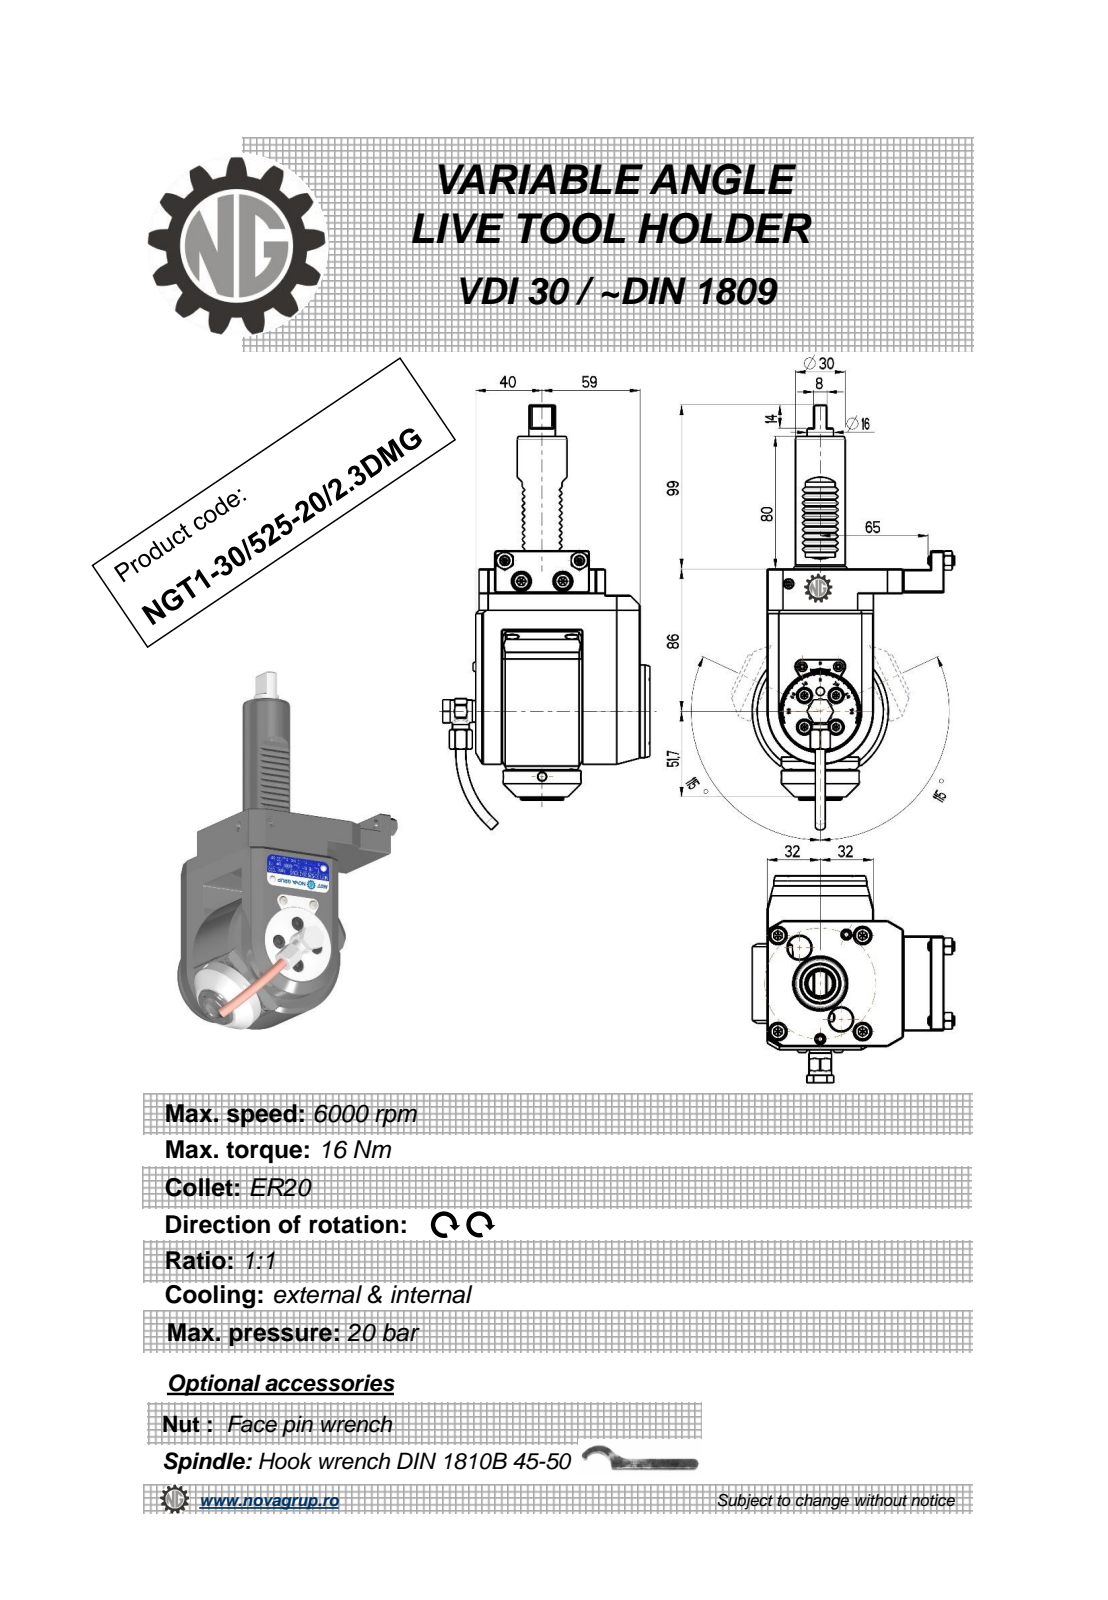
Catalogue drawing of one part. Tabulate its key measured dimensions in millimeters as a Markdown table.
| quantity | value |
| --- | --- |
| part name | NGT1_30_525_20_2_3DMG |
| STEP written by | PRO/ENGINEER BY PARAMETRIC TECHNOLOGY CORPORATION, 2010280 (CONFIG_CONTROL_DESIGN) |
| units | millimeters |
| bodies | 1 solid, 543 faces (251 planar, 136 cylindrical, 156 other) |
| overall size | 256.67 × 124.9 × 122 |
| volume | 845 728 mm³ |
| surface area | 81 277 mm² |
| round holes (diameter × count) | 3.2 × 4, 4 × 3, 5 × 2, 3 × 1, 6.2 × 1, 9 × 1, 10 × 1, 11 × 1, 16 × 1 |
| round bosses / shafts (diameter × count) | 6 × 4, 5.7 × 2, 56 × 1, 47 × 1, 36 × 1, 30 × 1, 26 × 1, 15.9 × 1 |
| partial cylindrical surfaces (radius × count) | 0.3 × 20, 0.31 × 10, 0.5 × 4, 0.8 × 2, 1 × 2, 7.7 × 1, 32 × 1, 41 × 1 |
| main face-to-face distances | 64, 14, 0.5, 37, 16, 99, 14.5, 62, 6, 105 |
| hole center spacings | 10.75, 15.2, 21.5, 50.17, 50.56, 0.4, 38.25, 38.65 |
